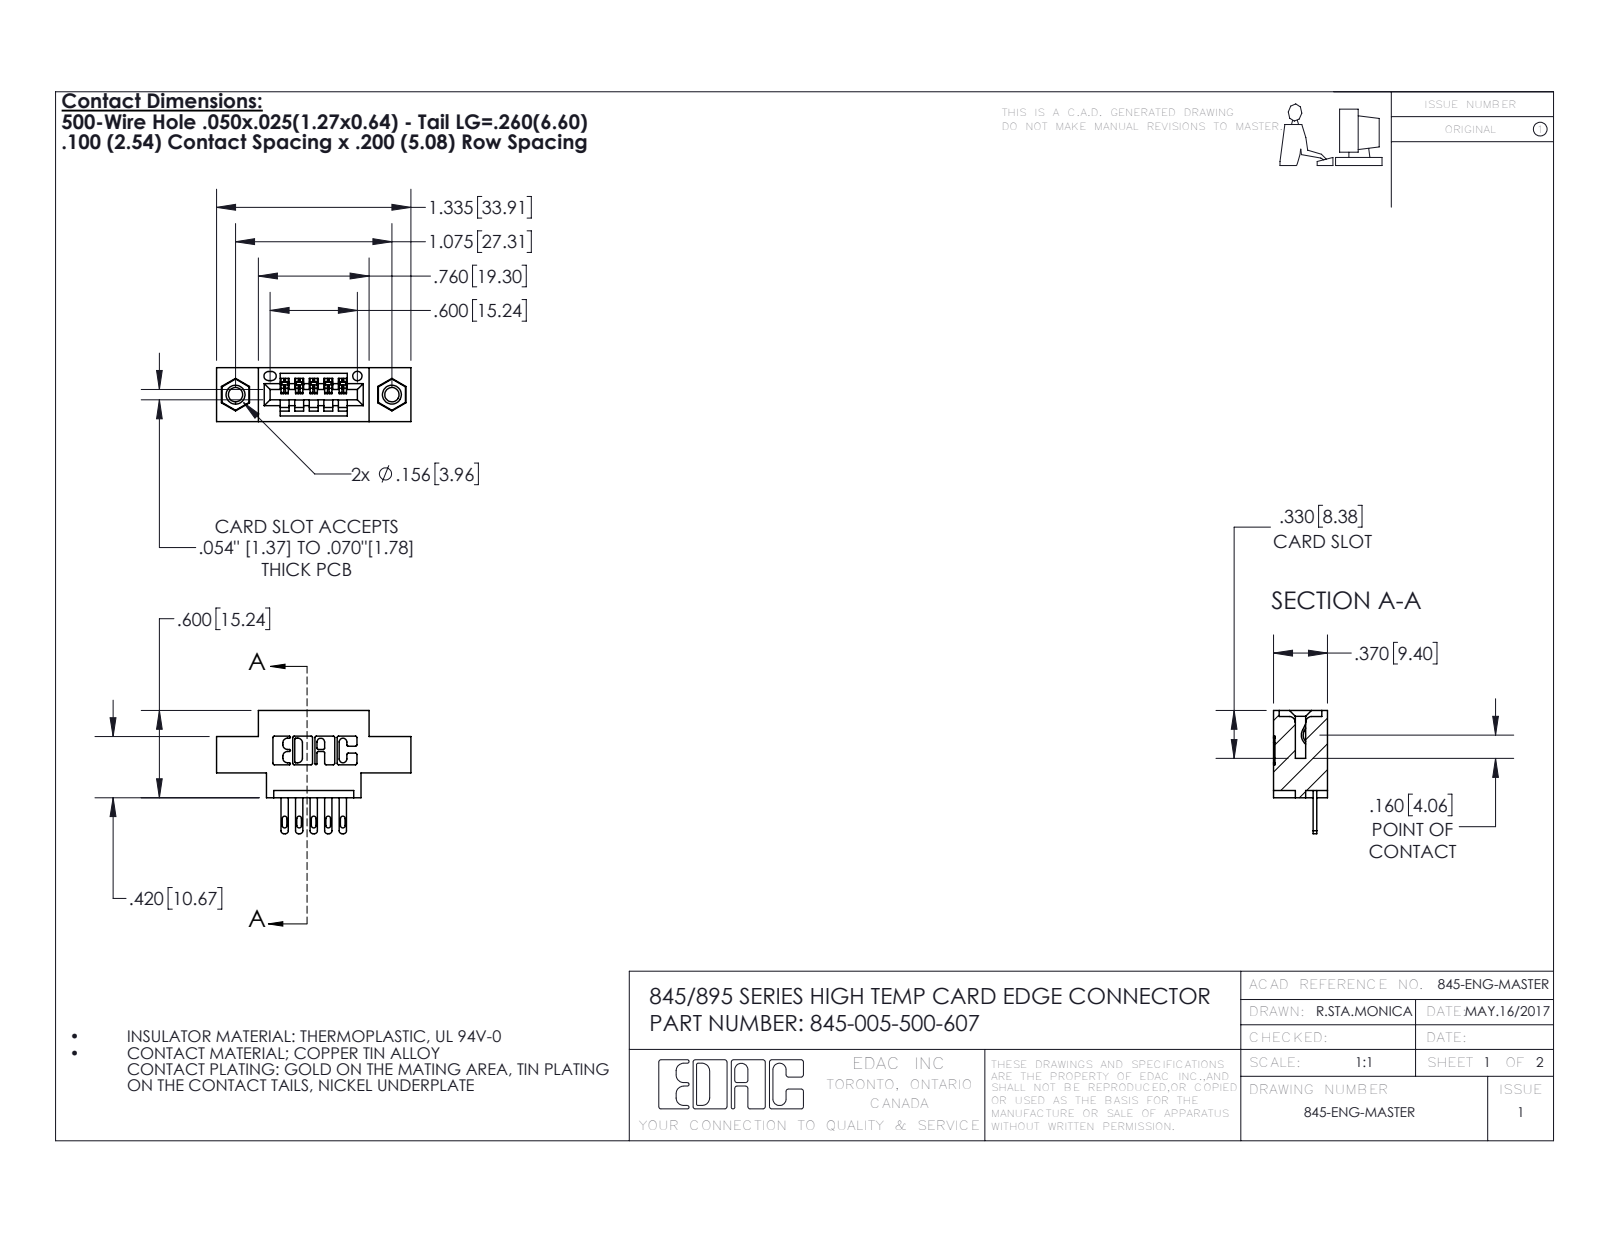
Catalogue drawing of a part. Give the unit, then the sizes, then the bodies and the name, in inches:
Units: inches
Overall size (bounding box): 1.335 × 0.847 × 0.37
Round holes (diameter × count): ⌀0.098 ×2, ⌀0.125 ×2, ⌀0.156 ×2, ⌀0.064 ×1
Round bosses / shafts (diameter × count): ⌀0.155 ×2
Partial cylindrical surfaces — rounded edges, fillets, slot ends (radius × count): R0.01 ×22, R0.006 ×10, R0.016 ×10, R0.02 ×10, R0.007 ×6, R0.031 ×6, R0.026 ×3, R0.031 ×2
Main face-to-face distances: 0.37, 0.2, 0.072, 0.298, 0.1, 0.025, 0.098, 0.272, 0.25, 0.06
Hole centre spacings: 0.27, 0.847, 1.075
Volume: 0.17 in³ · Surface area: 5.239 in²
Bodies: 8 solids, 460 faces (286 planar, 158 cylindrical, 16 other)
Part name (STEP PRODUCT): 345-250-001_345-250-005-103; 345 Part_0.170 Offset - 0.156 Dia-TI; 345-005-500-607; 345-292-001_345-293-100
STEP written by: SolidWorks 2016 (CONFIG_CONTROL_DESIGN)
